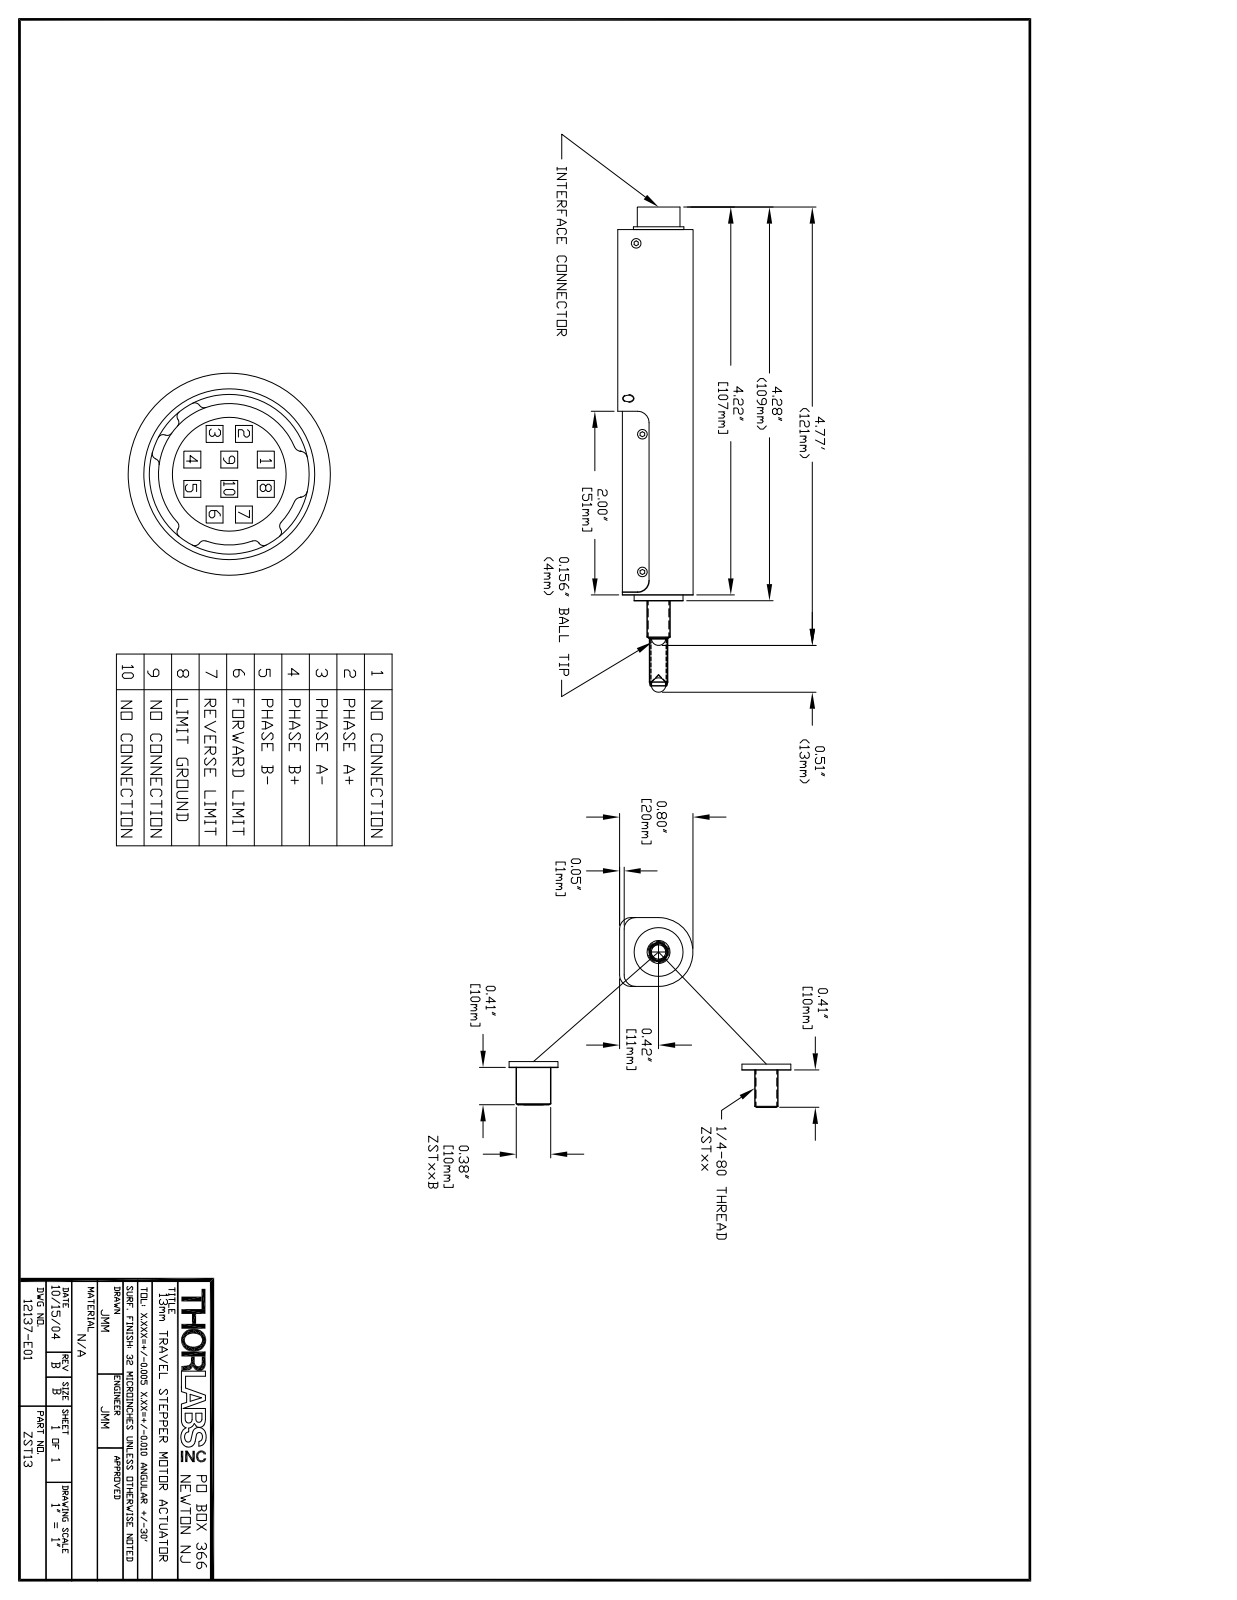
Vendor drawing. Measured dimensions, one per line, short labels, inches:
name: 12137-E0W
written by: SolidWorks 2007 (AUTOMOTIVE_DESIGN)
unit: in
bodies: 0 solids, 526 faces (126 planar, 347 cylindrical, 53 other)
size: 5.349 × 0.863 × 0.825
holes: 10× ⌀0.045, 3× ⌀0.14, 2× ⌀0.086, 1× ⌀0.156, 1× ⌀0.386
bosses: 6× ⌀0.139, 1× ⌀0.63, 1× ⌀0.551, 1× ⌀0.464, 1× ⌀0.3, 1× ⌀0.25, 1× ⌀0.23, 1× ⌀0.197
rounds: 6× R0.125, 3× R0.03, 1× R0.344, 1× R0.345, 1× R0.375
face distances: 0.75, 0.05, 0.03, 3.95, 3.98, 4.045, 4.015, 0.065, 0.26, 0.29
hole spacings: 0.071, 0.139, 0.1, 0.128, 0.158, 0.198, 0.08, 0.103
